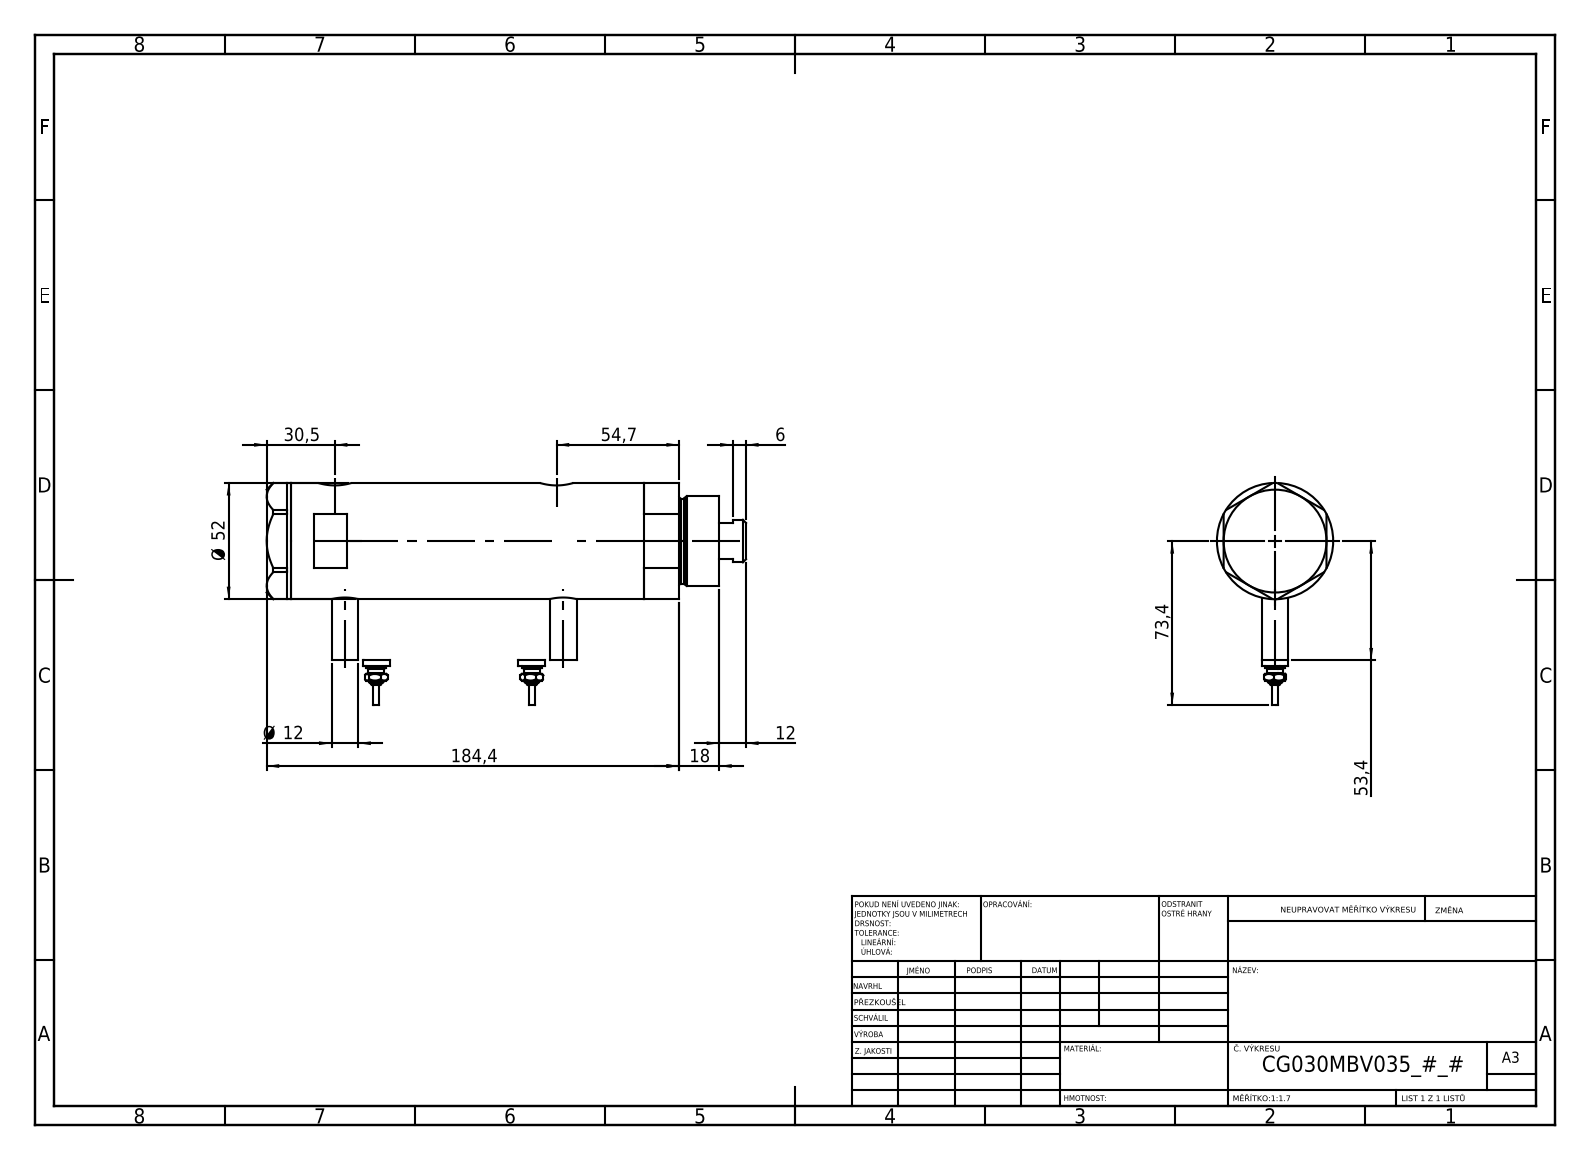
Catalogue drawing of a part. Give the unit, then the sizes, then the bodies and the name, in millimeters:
Units: millimetres
Overall size (bounding box): 214.4 × 99.4 × 52
Round holes (diameter × count): ⌀9.73 ×2, ⌀12.5 ×2, ⌀15 ×2, ⌀6.5 ×1, ⌀20 ×1, ⌀21.5 ×1, ⌀30 ×1, ⌀33 ×1, ⌀44 ×1
Round bosses / shafts (diameter × count): ⌀12 ×4, ⌀9 ×2, ⌀7 ×2, ⌀4.5 ×2, ⌀2.5 ×2, ⌀52 ×1, ⌀40 ×1, ⌀38 ×1
Main face-to-face distances: 121.5, 23.8, 97.7, 11, 34.8, 132.5, 46, 36.4, 168.9, 157.9
Hole centre spacings: 2.9, 4.5, 94.7, 97.6, 99.2, 102.1
Volume: 402 682 mm³ · Surface area: 90 312 mm²
Bodies: 6 solids, 226 faces (93 planar, 69 cylindrical, 64 other)
Part name (STEP PRODUCT): V270CG_FRONT; Switch; V270CG_MIDDLE; V270CG_VC (+1 more)
STEP written by: SolidWorks 2019 (CONFIG_CONTROL_DESIGN)
